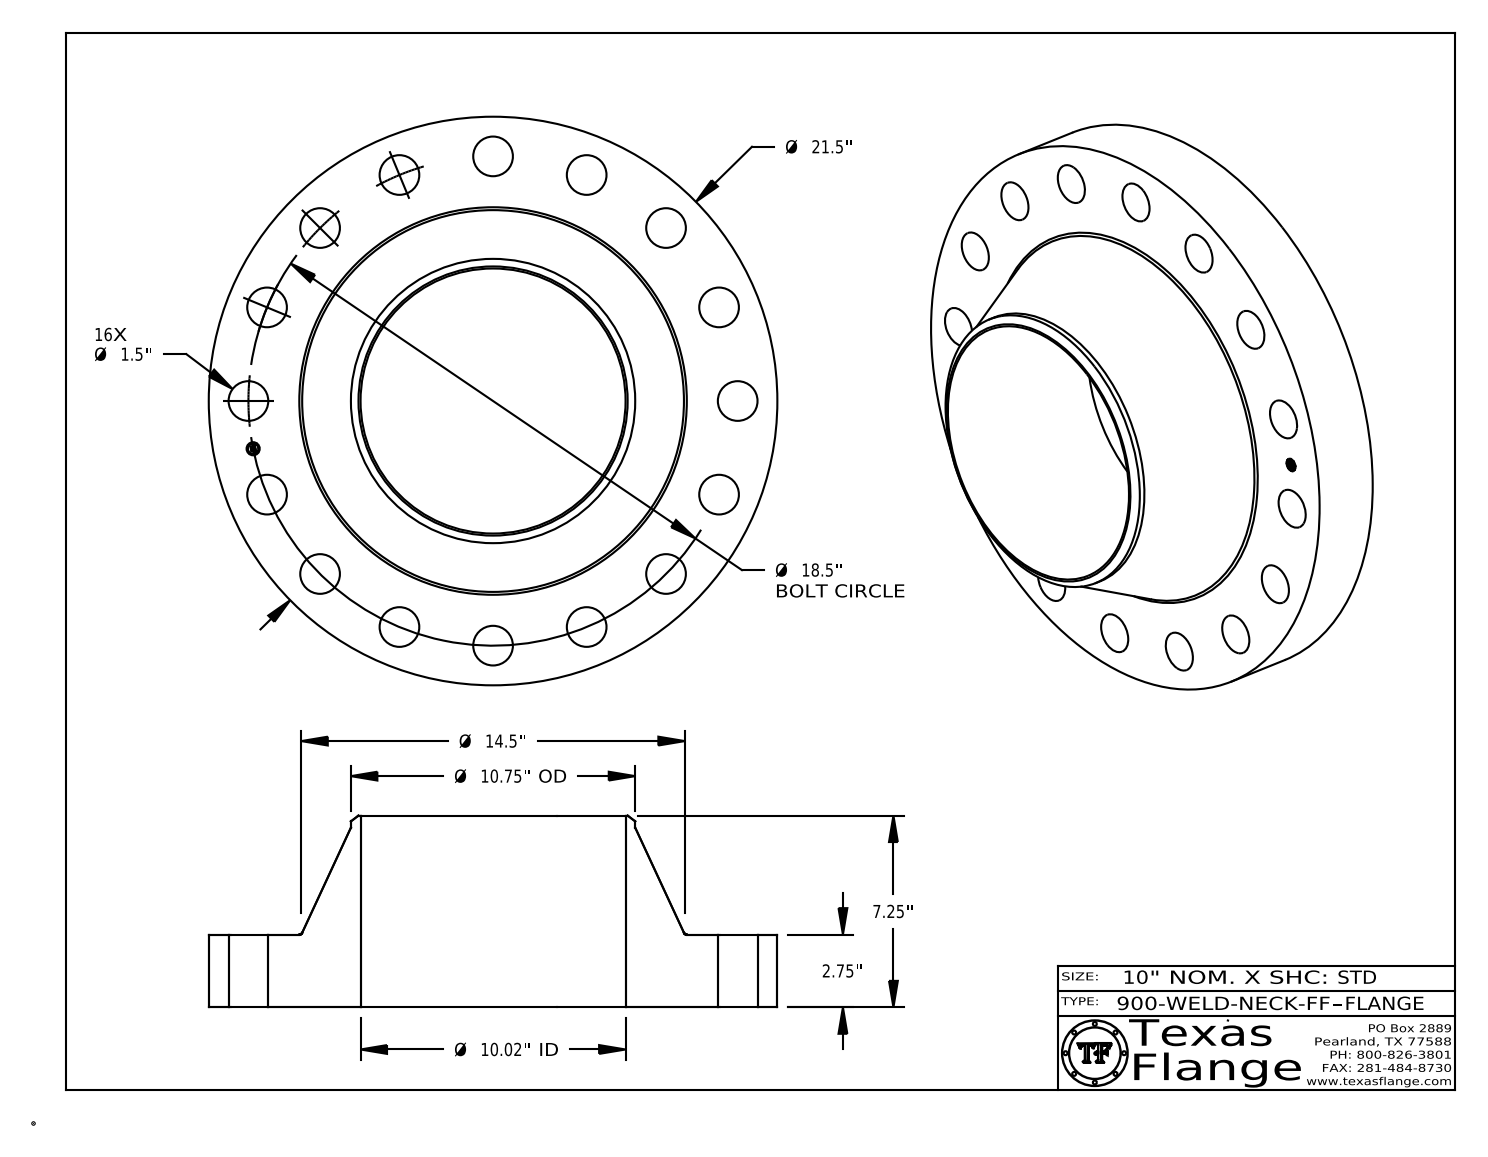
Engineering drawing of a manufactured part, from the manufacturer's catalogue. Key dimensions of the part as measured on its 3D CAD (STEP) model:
Part name (STEP PRODUCT): 900-WELD-NECK-FF
STEP written by: CATIA V5 STEP AP214 (AUTOMOTIVE_DESIGN)
Units: inches
Bodies: 1 solid, 432 faces (368 planar, 58 cylindrical, 6 other)
Overall size (bounding box): 21.5 × 21.5 × 7.25
Volume: 899.3 in³ · Surface area: 1 245 in²
Round holes (diameter × count): ⌀1.5 ×16, ⌀0.495 ×1, ⌀10.02 ×1
Round bosses / shafts (diameter × count): ⌀0.03 ×8, ⌀21.5 ×1, ⌀10.75 ×1, ⌀0.39 ×1
Main face-to-face distances: 2.75, 7.25, 4.5, 2.735, 0.015, 4.515, 0.148, 0.145, 0.027, 0.096
Hole centre spacings: 15.382, 7.08, 9.25, 13.081, 3.609, 3.609, 10.278, 10.278
